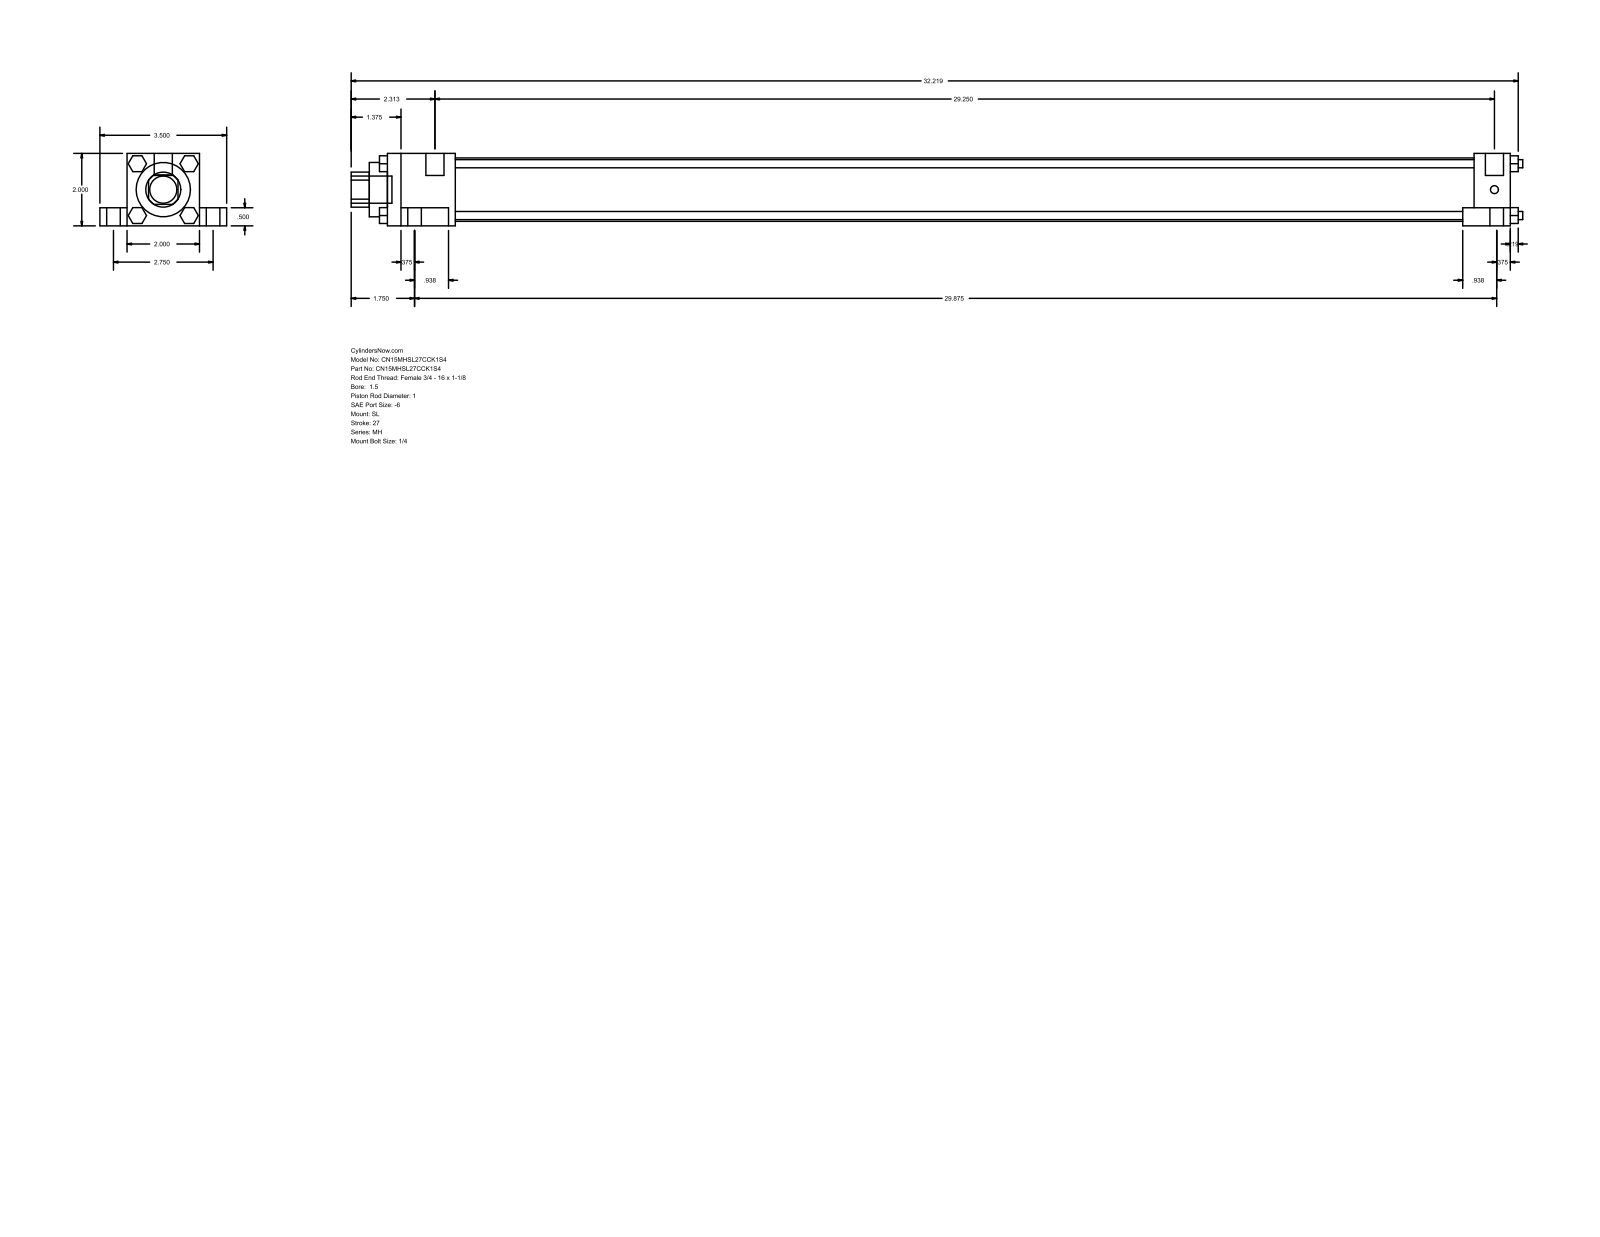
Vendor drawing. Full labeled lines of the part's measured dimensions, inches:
Part name (STEP PRODUCT): MH_SL__0150_1
STEP written by: GSSL Pune (CONFIG_CONTROL_DESIGN)
Units: inches
Bodies: 0 solids, 148 faces (112 planar, 36 cylindrical, 0 other)
Overall size (bounding box): 32.344 × 3.5 × 2
Round holes (diameter × count): ⌀1 ×1, ⌀1.5 ×1, ⌀1.75 ×1
Round bosses / shafts (diameter × count): ⌀0.625 ×4, ⌀0.375 ×4, ⌀0.225 ×4, ⌀0.219 ×4, ⌀0.5 ×2, ⌀0.75 ×1
Partial cylindrical surfaces — rounded edges, fillets, slot ends (radius × count): R0.484 ×1
Main face-to-face distances: 2, 0.5, 1.5, 0.75, 2.75, 31, 1, 0.375, 1.313, 29.313
